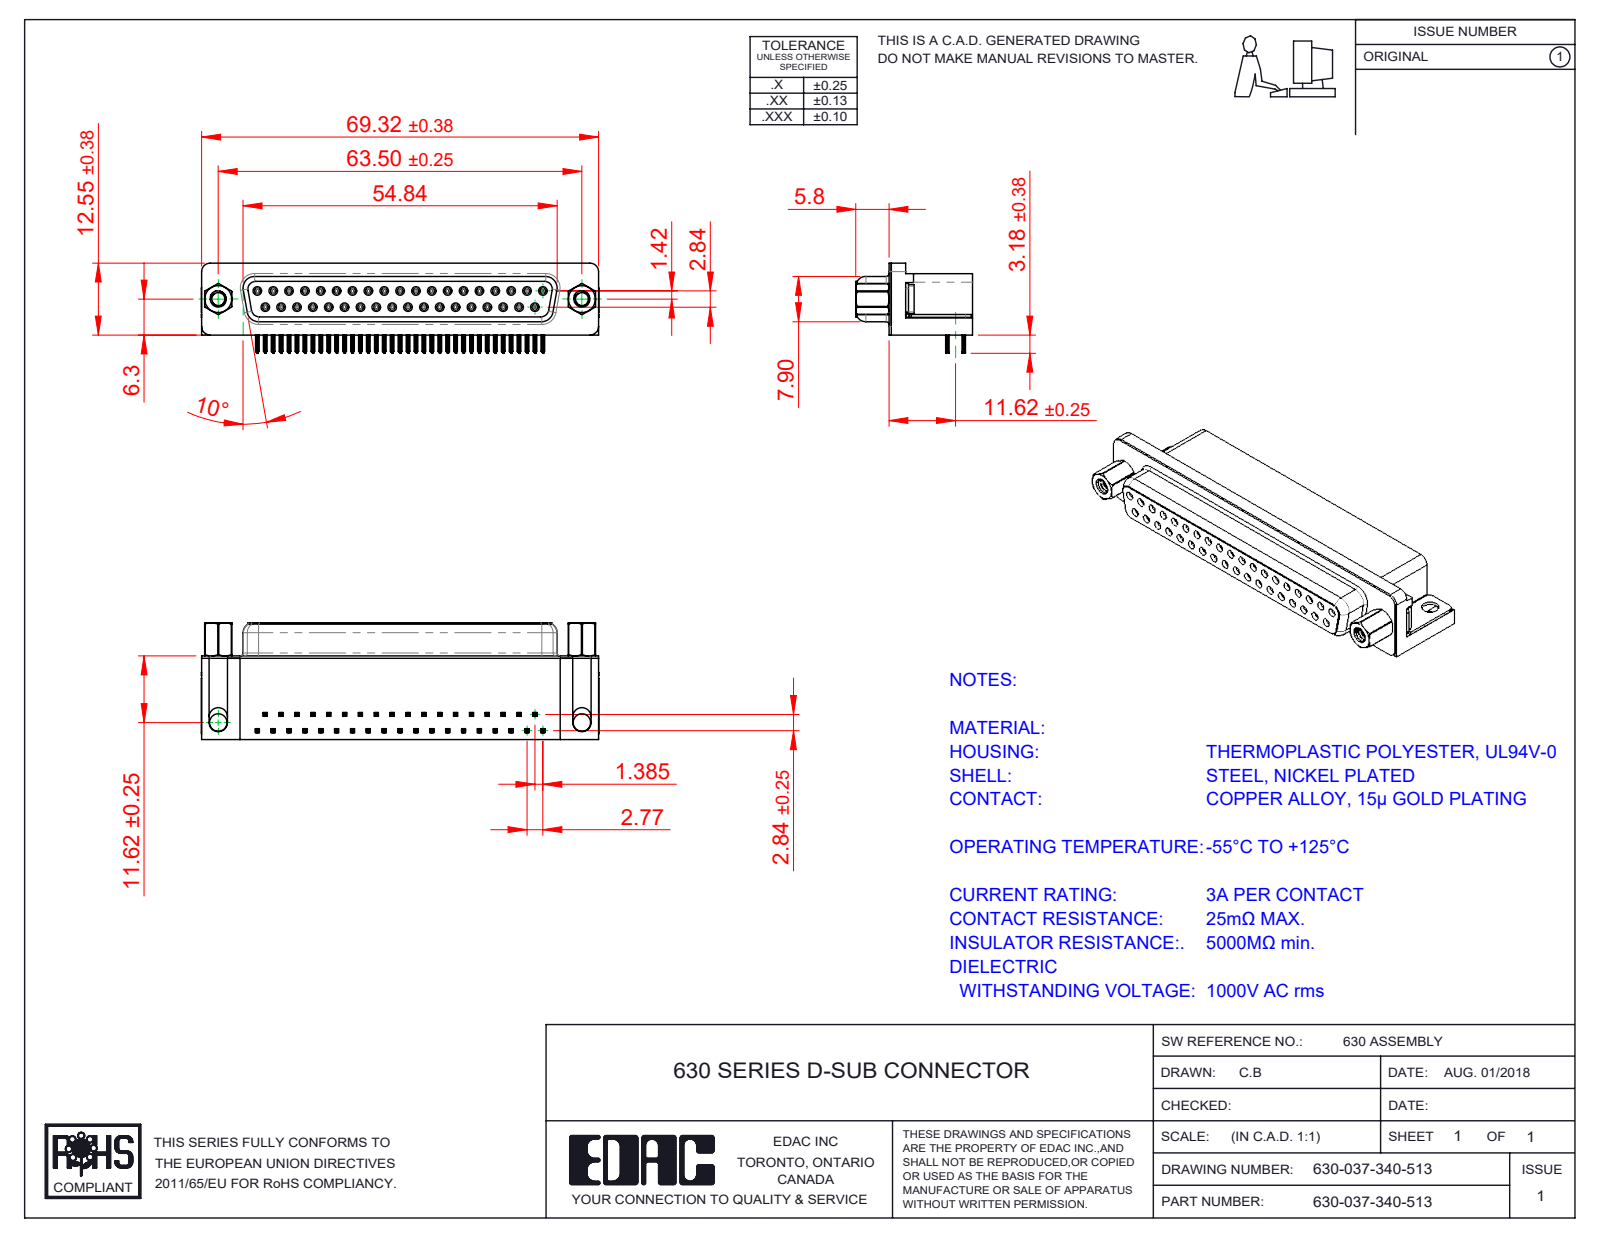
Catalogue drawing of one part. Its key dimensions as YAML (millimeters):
part_name: "630 Contact Top; 630-037-340-513; 630 Thru Hole Board Mount; 630 Shell_37 Socket (+4 more)"
step_written_by: "SolidWorks 2020 (CONFIG_CONTROL_DESIGN)"
units: millimeters
bodies: {solids: 45, faces: 5686, planar: 2524, cylindrical: 1370, other: 1792}
overall_size: [69.4, 20.4, 15.73]
volume: 12027
surface_area: 14018
round_holes:
  - {diameter: 0.8, count: 37}
  - {diameter: 0.9, count: 37}
  - {diameter: 2.26, count: 2}
  - {diameter: 2.29, count: 2}
  - {diameter: 3.05, count: 2}
  - {diameter: 4, count: 2}
  - {diameter: 4.8, count: 2}
  - {diameter: 5, count: 2}
round_bosses_or_shafts:
  - {diameter: 1.2, count: 37}
  - {diameter: 4.9, count: 2}
  - {diameter: 4.75, count: 2}
  - {diameter: 3.9, count: 2}
  - {diameter: 2.79, count: 2}
partial_cylinders:
  - {radius: 0.1, count: 296}
  - {radius: 0.15, count: 148}
  - {radius: 0.35, count: 74}
  - {radius: 0.34, count: 37}
  - {radius: 0.28, count: 18}
  - {radius: 1, count: 18}
  - {radius: 0.25, count: 8}
  - {radius: 1.35, count: 8}
face_to_face_distances: [0.4, 6.2, 10.34, 14.2, 6.65, 0.85, 2.84, 14.6, 0.45, 5.8]
hole_center_spacings: [3.16, 2.77, 5.54, 8.31, 11.08, 13.85, 16.62, 19.39]
